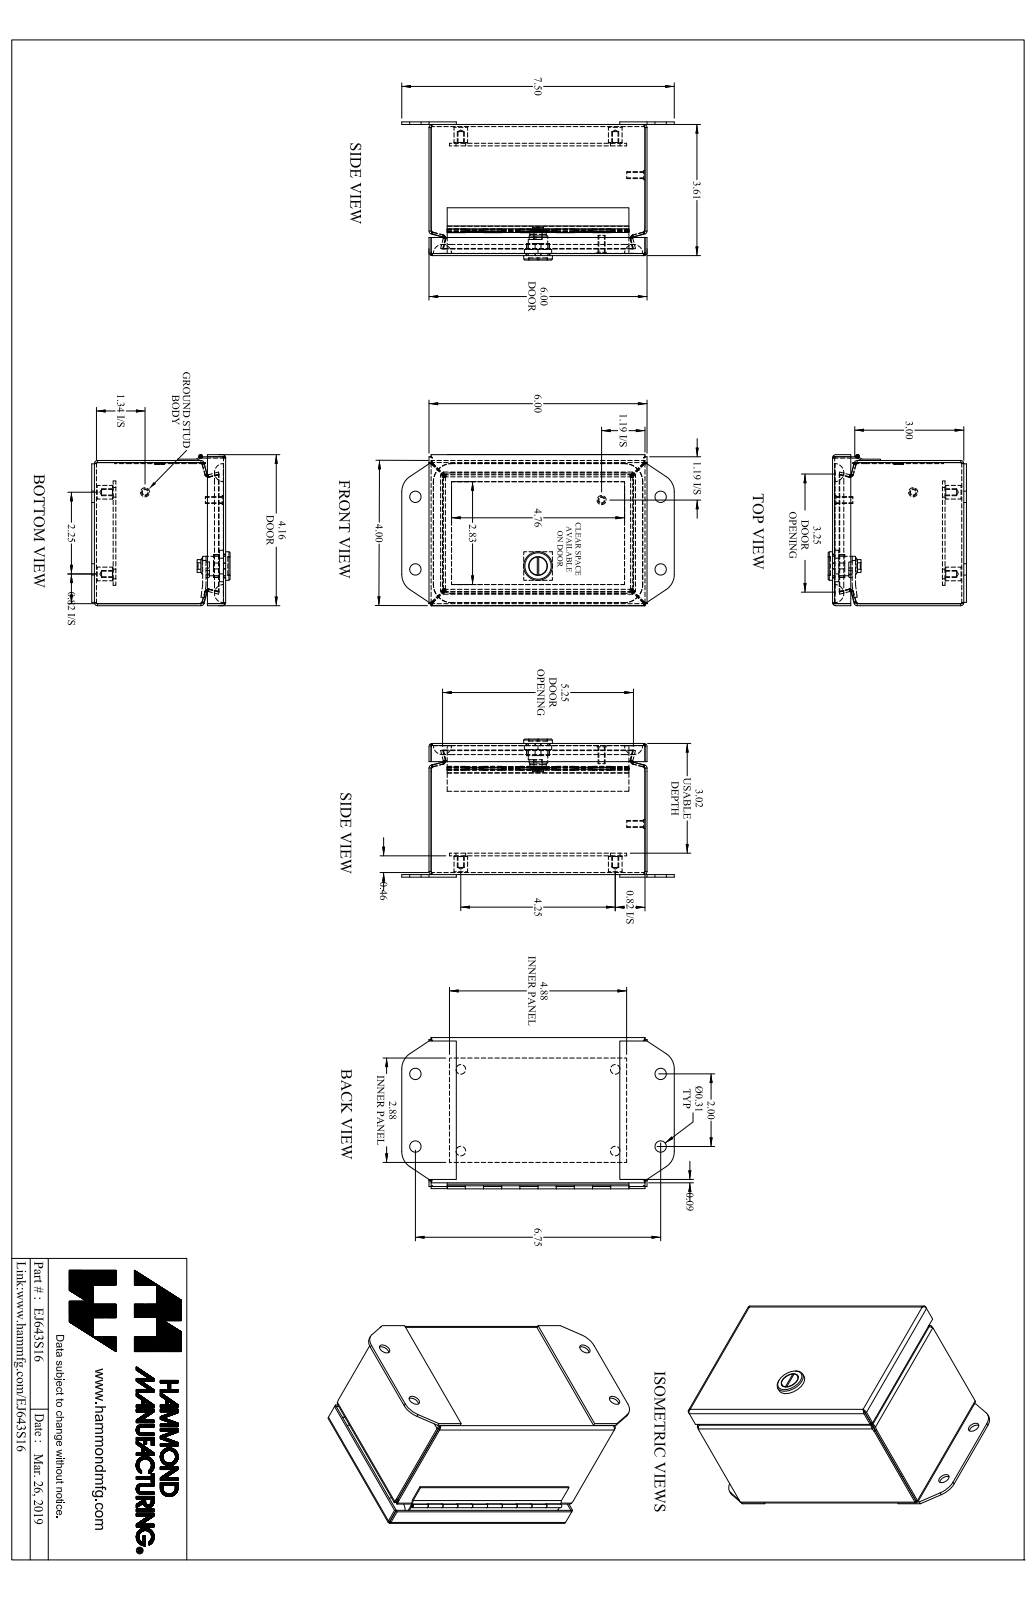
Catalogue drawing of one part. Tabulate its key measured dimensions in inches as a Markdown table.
| quantity | value |
| --- | --- |
| part name | EJ643S16_Default |
| STEP written by | SolidWorks 2019 (CONFIG_CONTROL_DESIGN) |
| units | inches |
| bodies | 16 solids, 532 faces (278 planar, 174 cylindrical, 80 other) |
| overall size | 7.5 × 4.165 × 3.805 |
| volume | 11.29 in³ |
| surface area | 370.5 in² |
| round holes (diameter × count) | 0.156 × 4, 0.265 × 4, 0.313 × 4, 0.05 × 1, 0.516 × 1 |
| round bosses / shafts (diameter × count) | 0.375 × 4, 0.25 × 2, 0.19 × 2, 0.788 × 1, 0.535 × 1, 0.496 × 1, 0.435 × 1, 0.1 × 1 |
| partial cylindrical surfaces (radius × count) | 0.029 × 16, 0.086 × 16, 0.281 × 12, 0.25 × 4, 0.499 × 4, 0.5 × 4, 0.06 × 2, 0.03 × 1 |
| main face-to-face distances | 0.057, 3.554, 3.943, 5.943, 0.072, 0.589, 3.611, 3.497, 3.886, 4 |
| hole center spacings | 1.257, 5.502, 4.25, 2.465, 2.94, 5.896, 2, 2.136 |
